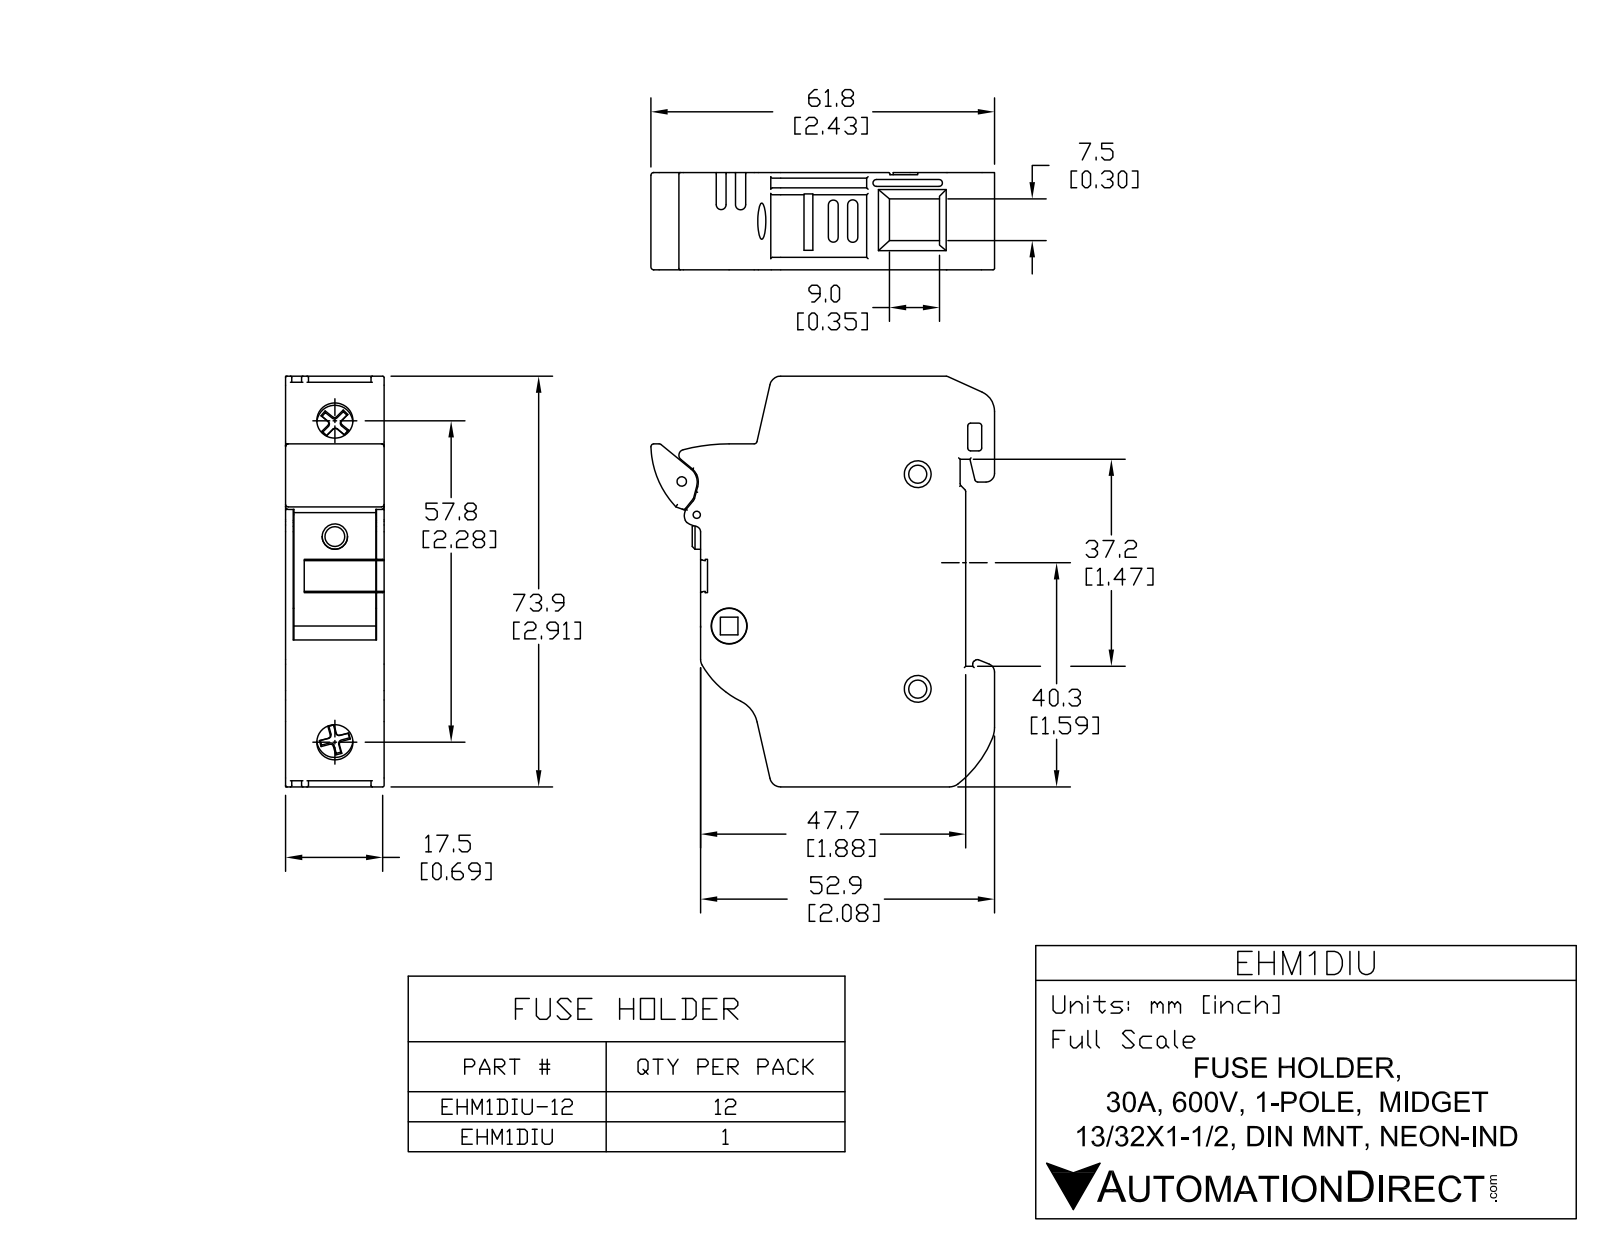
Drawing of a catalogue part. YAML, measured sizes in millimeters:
part_name: "EHM1DIU"
step_written_by: "SolidWorks 2011 (AUTOMOTIVE_DESIGN)"
units: millimeters
bodies: {solids: 2, faces: 597, planar: 247, cylindrical: 198, other: 152}
overall_size: [73.88, 61.82, 17.5]
volume: 52741
surface_area: 19587
round_holes:
  - {diameter: 3.25, count: 2}
  - {diameter: 4.83, count: 2}
  - {diameter: 6.5, count: 2}
  - {diameter: 1.3, count: 1}
  - {diameter: 1.7, count: 1}
  - {diameter: 6.48, count: 1}
round_bosses_or_shafts:
  - {diameter: 6.35, count: 1}
  - {diameter: 4.55, count: 1}
partial_cylinders:
  - {radius: 0.25, count: 60}
  - {radius: 0.5, count: 21}
  - {radius: 2, count: 10}
  - {radius: 0.51, count: 9}
  - {radius: 1, count: 7}
  - {radius: 0.62, count: 4}
  - {radius: 0.89, count: 3}
  - {radius: 0.92, count: 3}
face_to_face_distances: [17.5, 1.25, 1.58, 16.25, 1.37, 16.13, 14.88, 27.51, 29.09, 22.94]
hole_center_spacings: [6.58, 20.83, 27.36, 35.77, 35.79, 38.61, 38.66, 40.43]
